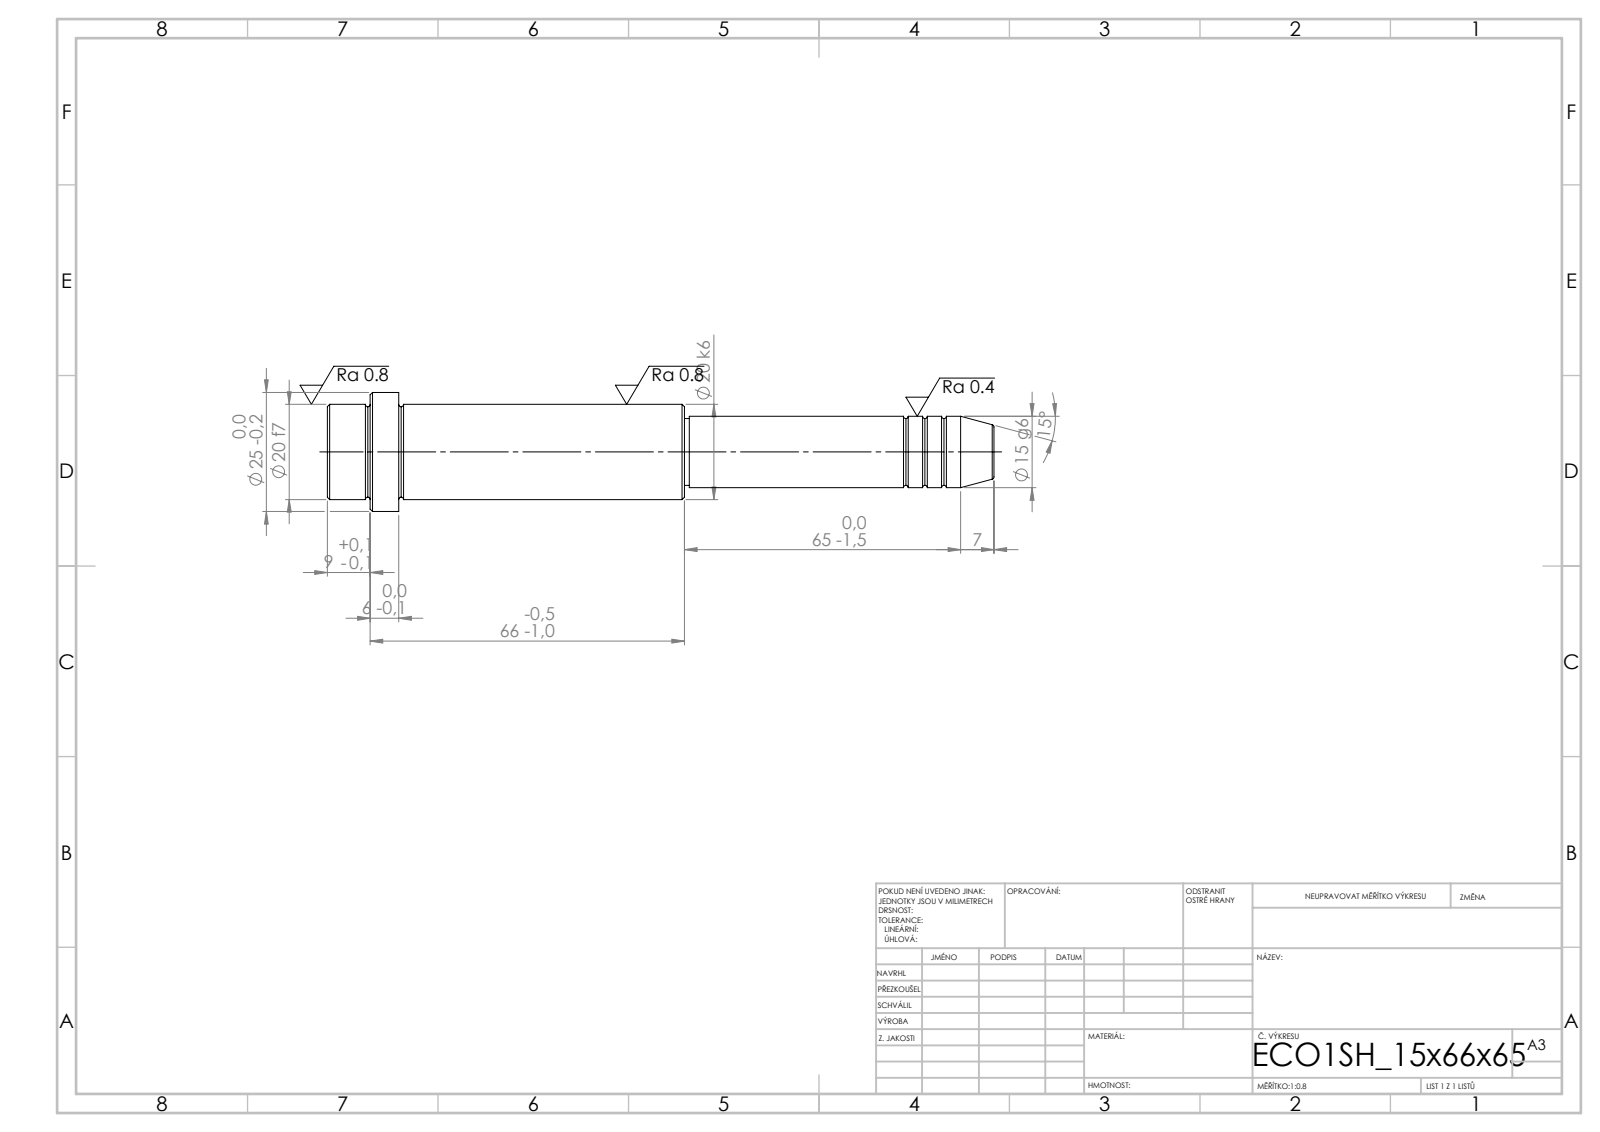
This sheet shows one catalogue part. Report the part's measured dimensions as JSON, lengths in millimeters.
{"step_written_by": "SolidWorks 2019 (CONFIG_CONTROL_DESIGN)", "units": "millimeters", "bodies": {"solids": 1, "faces": 52, "planar": 6, "cylindrical": 16, "other": 30}, "overall_size": [140, 25, 25], "volume_mm3": 35674, "surface_area_mm2": 8857, "round_bosses_or_shafts": [[25, 1], [20, 1], [15, 1], [14, 1]], "face_to_face_distances": [15, 6, 9, 60, 66, 75, 65, 125, 131, 140]}
